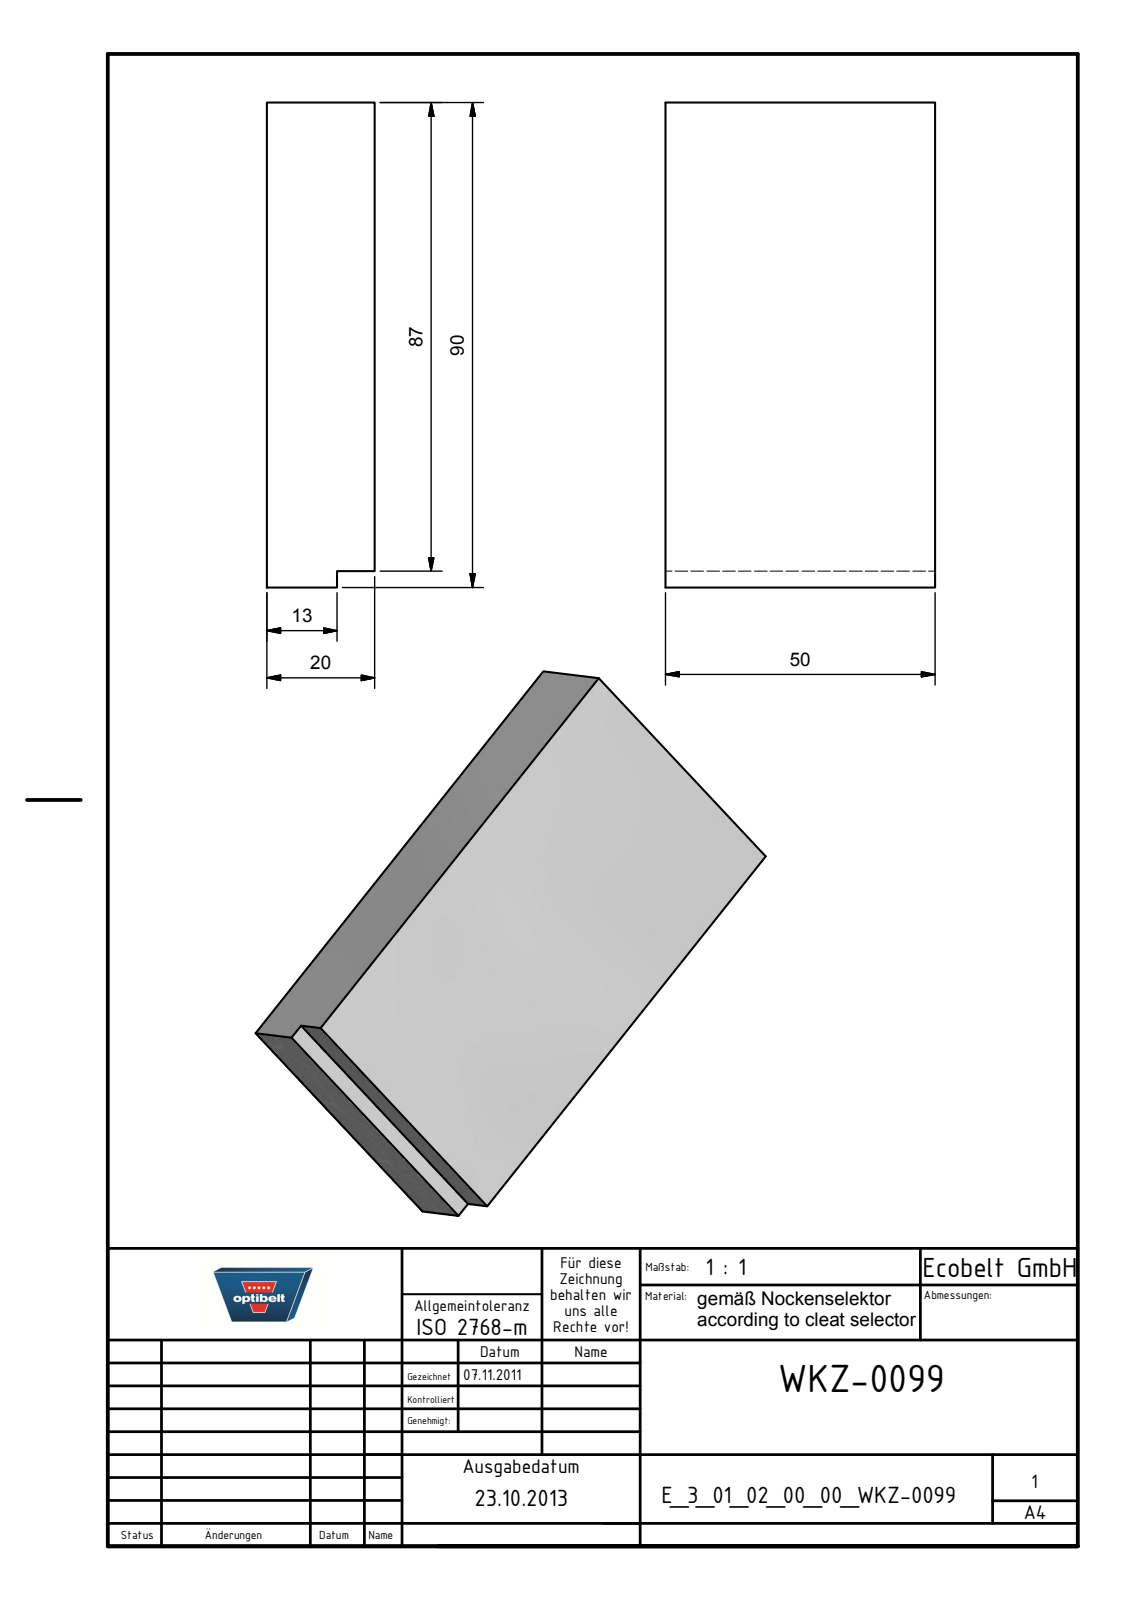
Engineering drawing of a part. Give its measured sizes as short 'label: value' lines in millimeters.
name: E_3_01_02_00_00_WKZ-0099
written by: Autodesk Inventor 2021 (AUTOMOTIVE_DESIGN)
unit: mm
bodies: 1 solid, 8 faces (8 planar, 0 cylindrical, 0 other)
size: 90 × 50 × 20
volume: 88 950 mm³; area: 14 558 mm²
face distances: 20, 50, 90, 3, 87, 13, 7
